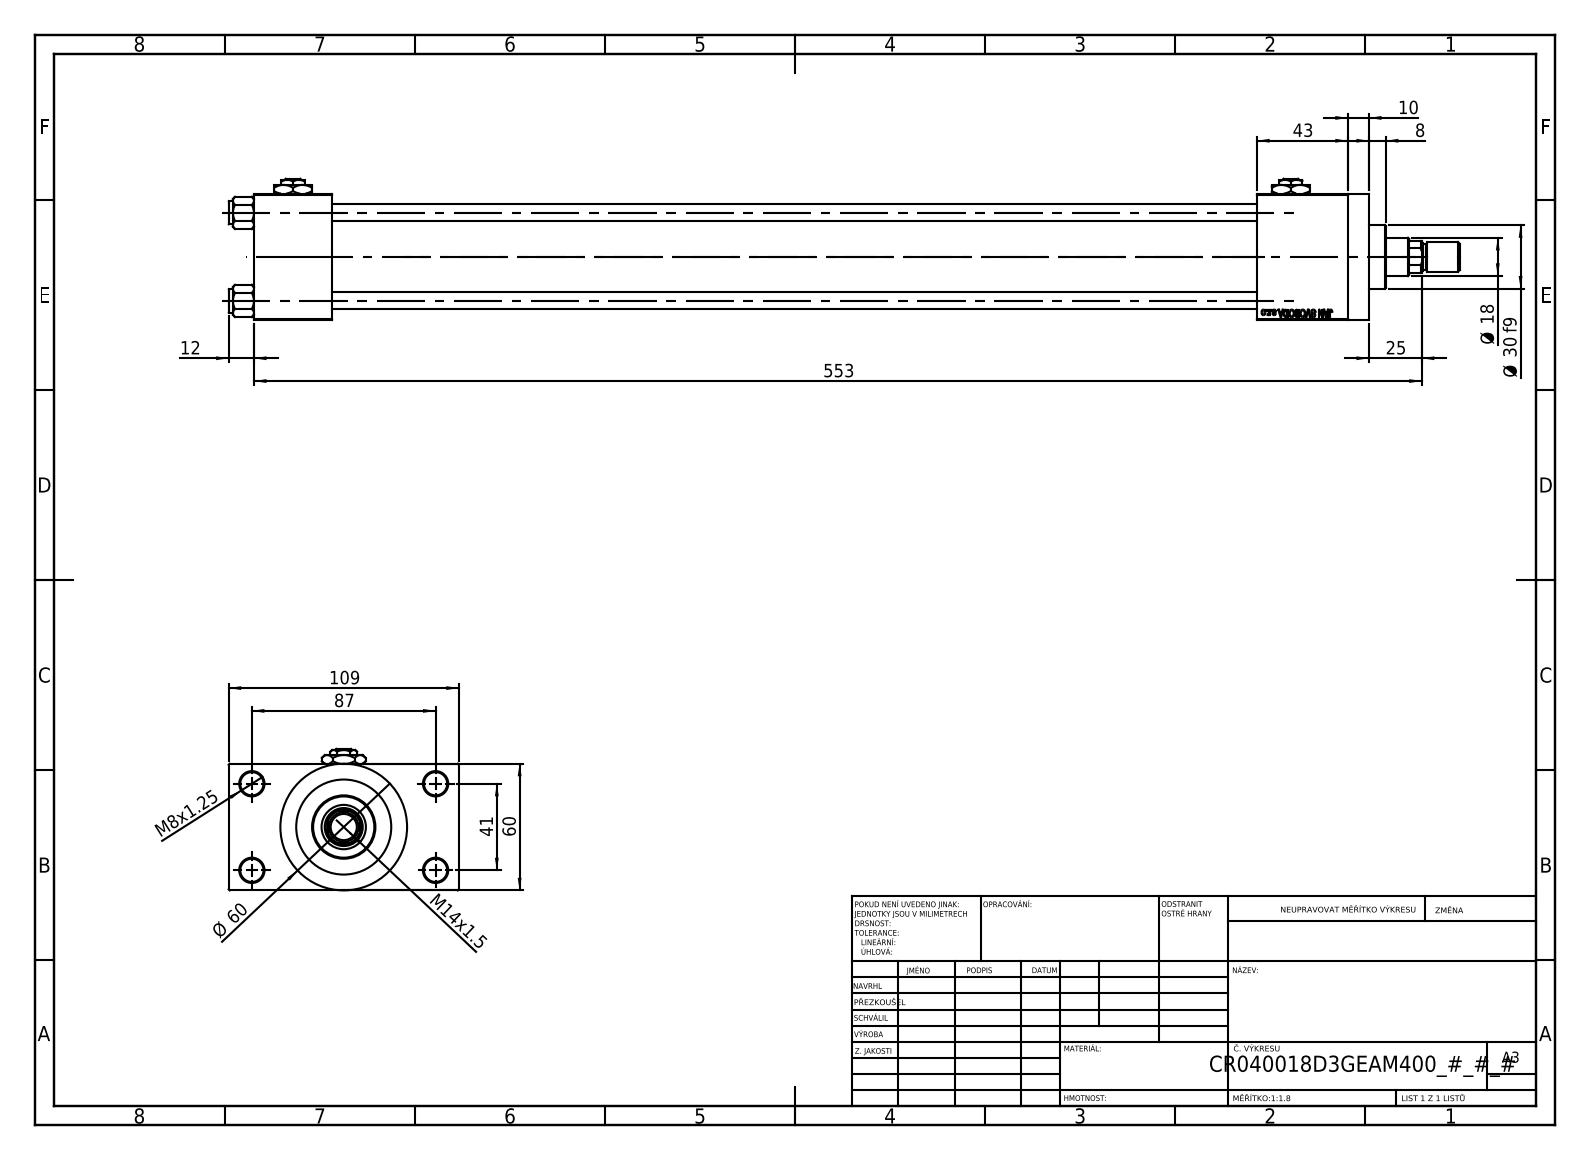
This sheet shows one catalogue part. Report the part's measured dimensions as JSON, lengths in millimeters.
{"part_name": "V215CR_D_Body; V215_VC_A; Zatka_pro_OIL_PORT; NUT_M5_D (+3 more)", "step_written_by": "SolidWorks 2019 (CONFIG_CONTROL_DESIGN)", "units": "millimeters", "bodies": {"solids": 14, "faces": 1220, "planar": 550, "cylindrical": 104, "other": 566}, "overall_size": [583, 109, 67], "volume_mm3": 845366, "surface_area_mm2": 287399, "round_holes": [[8, 4], [11, 4], [7, 2], [16.66, 2], [24, 2], [8.5, 1], [18, 1], [21, 1], [31, 1], [40, 1], [45, 1]], "round_bosses_or_shafts": [[11, 4], [60, 1], [46, 1], [30, 1], [14, 1], [12, 1]], "partial_cylinders_radius": [[8.5, 1]], "face_to_face_distances": [60, 24.5, 84.5, 438, 37, 475, 43, 518, 481, 109], "hole_center_spacings": [22.65, 29.49, 41.7, 47.15, 48.09, 64.35, 76.49, 41]}
